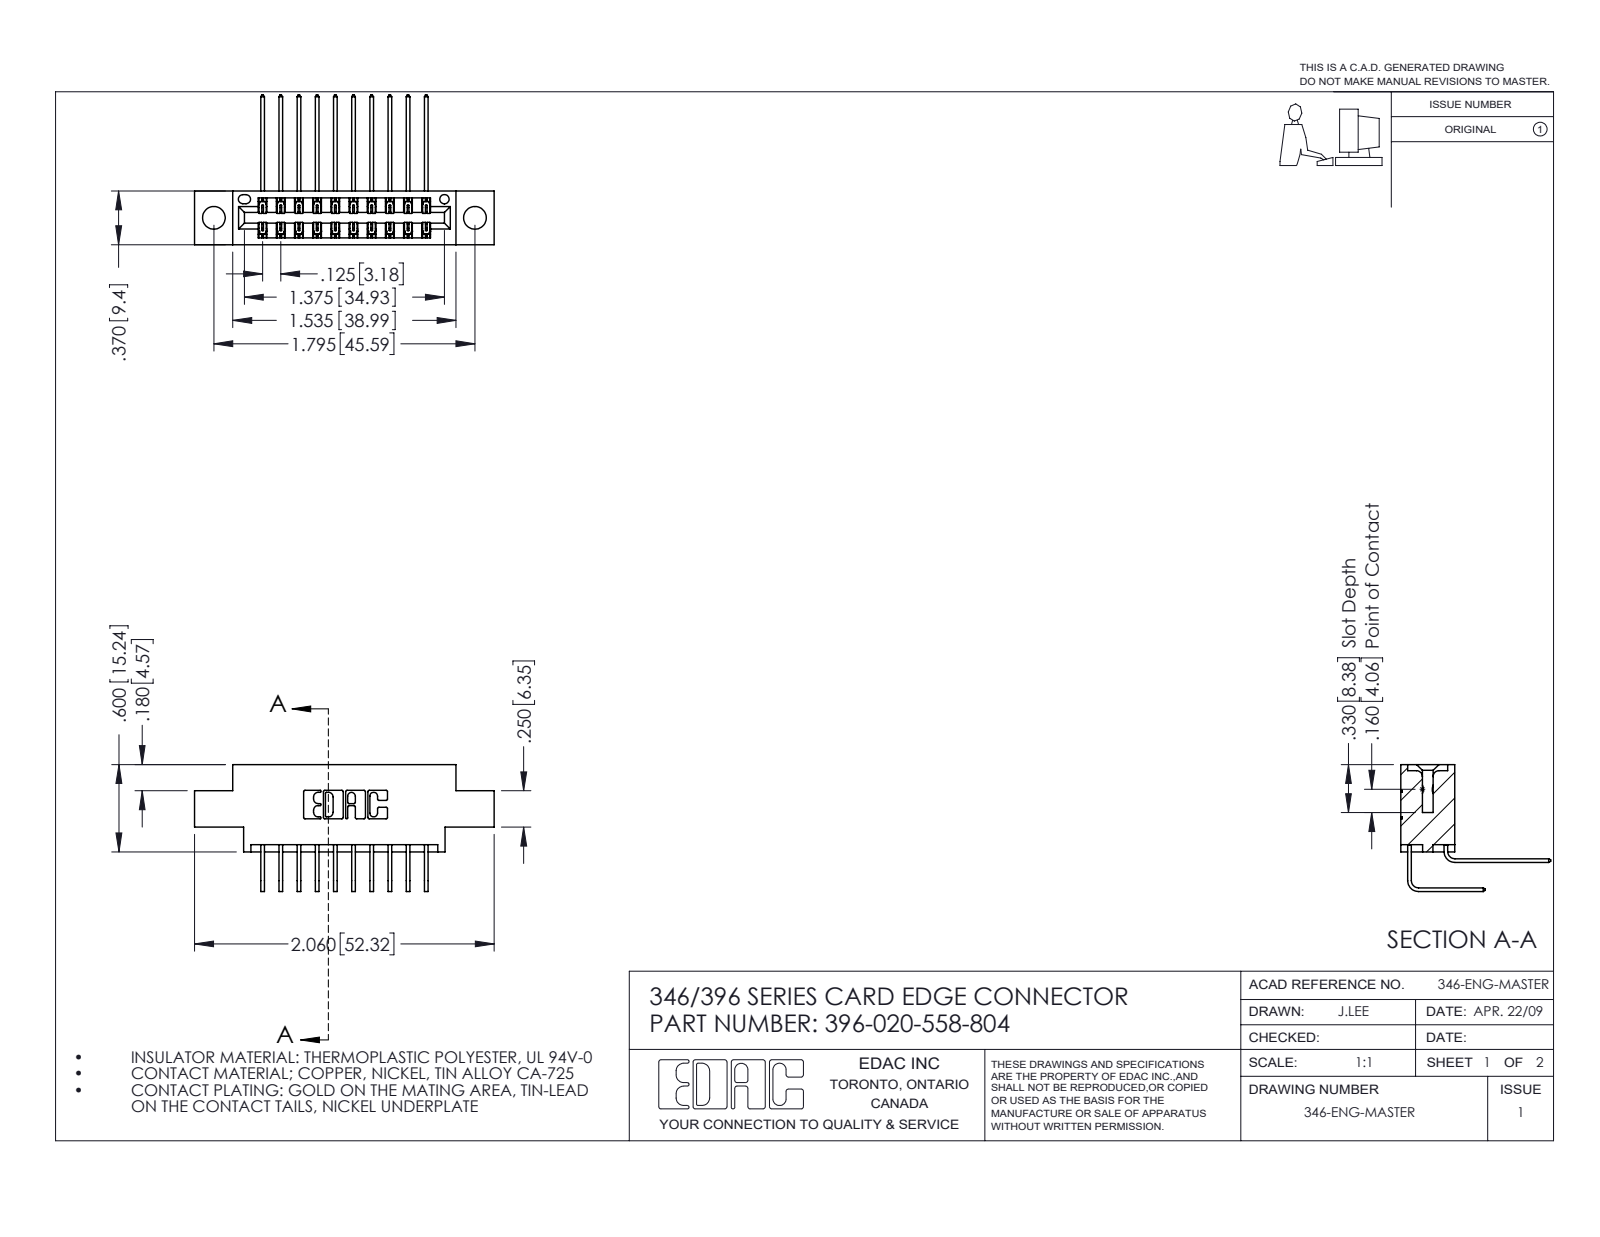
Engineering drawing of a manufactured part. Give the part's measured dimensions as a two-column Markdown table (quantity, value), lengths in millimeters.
| quantity | value |
| --- | --- |
| part name | 396-020-558-804; 345-292-001_558 559 Tail - 1; 346 Part_0.170 Offset - 0.156 Dia-TH; 345-292-001_558 Tail - 2 |
| STEP written by | SolidWorks 2016 (CONFIG_CONTROL_DESIGN) |
| units | millimeters |
| bodies | 21 solids, 1206 faces (820 planar, 386 cylindrical, 0 other) |
| overall size | 52.3 × 26.2 × 22.2 |
| volume | 4 720 mm³ |
| surface area | 6 542 mm² |
| round holes (diameter × count) | 4 × 2, 1.6 × 1 |
| partial cylindrical surfaces (radius × count) | 0.2 × 30, 0.3 × 22, 0.2 × 6, 0.8 × 6, 0.7 × 3, 0.4 × 2, 0.6 × 2, 0.6 × 2 |
| main face-to-face distances | 6.4, 1.2, 8.2, 9.4, 0.6, 1.8, 7.6, 7, 3.8, 5.6 |
| hole center spacings | 6.2, 40.4, 45.6 |
